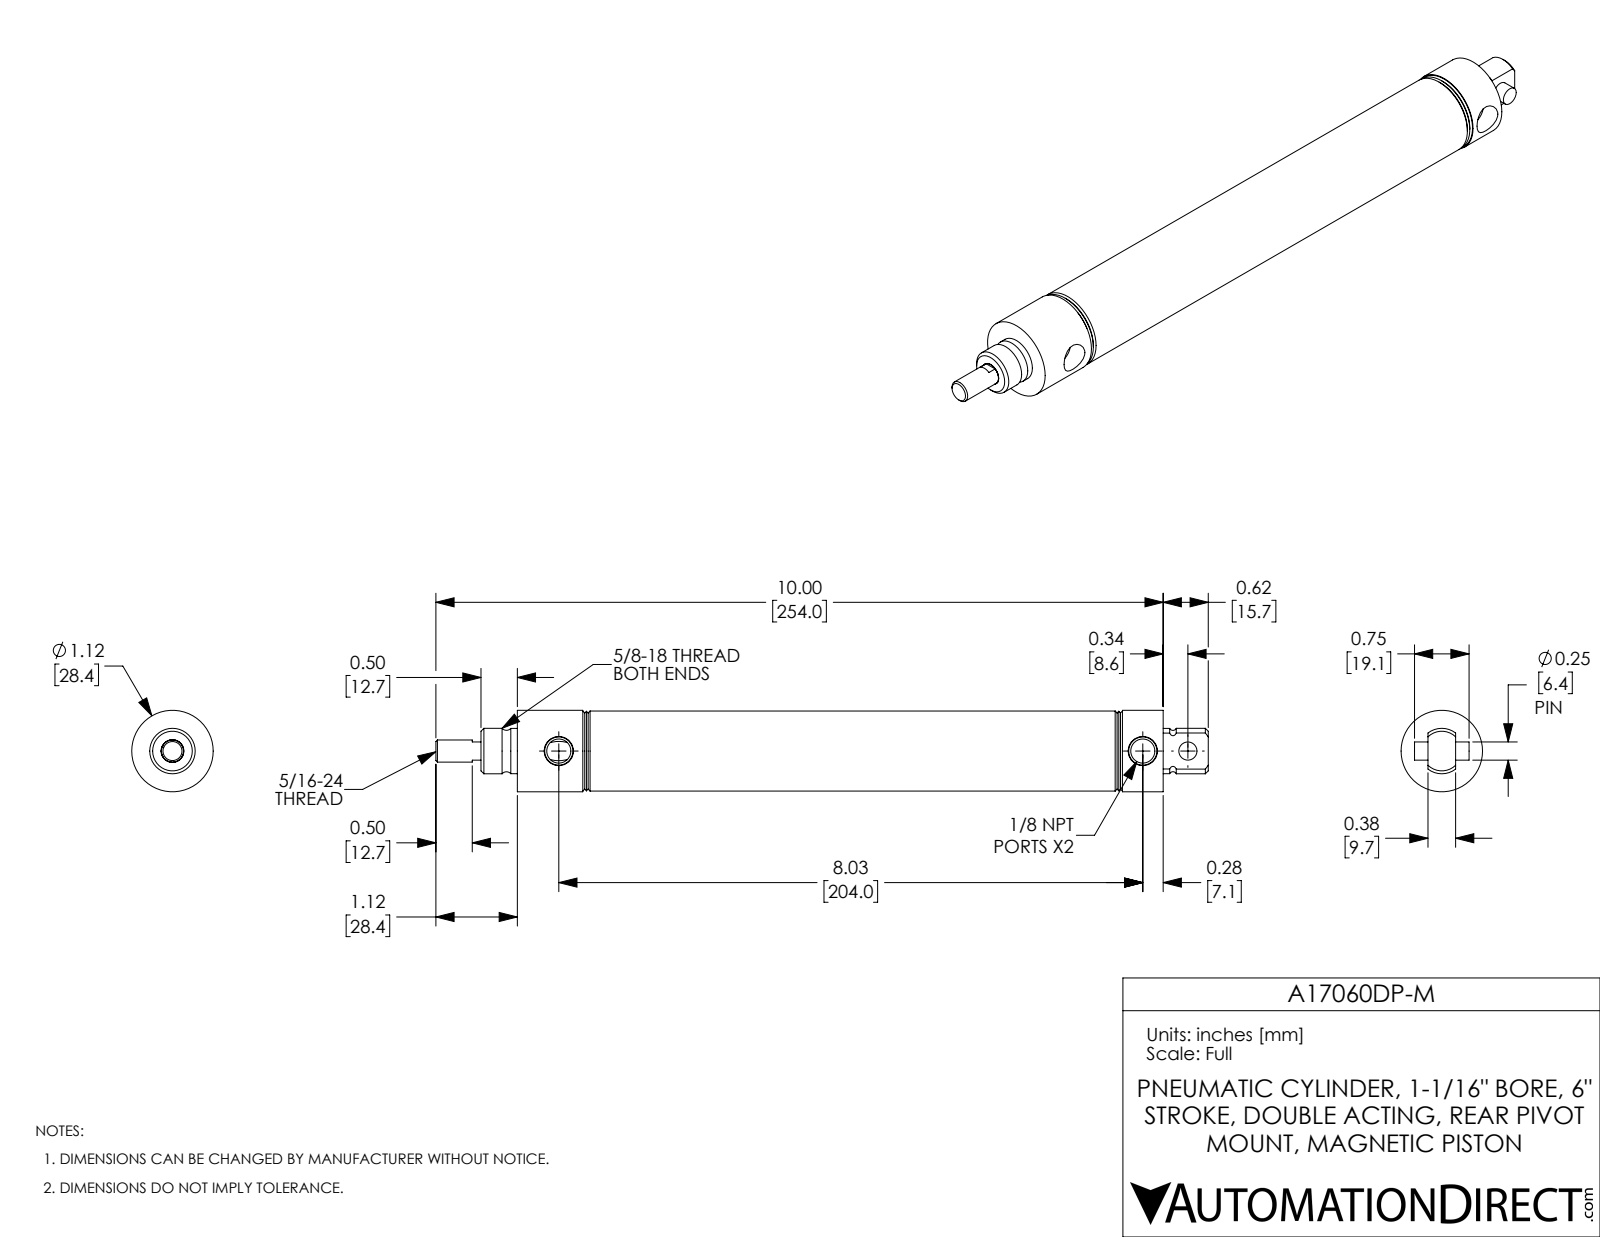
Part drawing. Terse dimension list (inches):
name: A17060DP-M-Rod; A17060DP-M-MainBody; A17060DP-M; A17060DP-M-PIN
written by: SolidWorks 2017 (AUTOMOTIVE_DESIGN)
unit: in
bodies: 3 solids, 92 faces (22 planar, 32 cylindrical, 38 other)
size: 10.62 × 1.12 × 1.12
volume: 3.867 in³; area: 73.4 in²
holes: 2× ⌀0.332, 1× ⌀0.25, 1× ⌀0.312, 1× ⌀1.063
bosses: 1× ⌀1.12, 1× ⌀1.1, 1× ⌀0.625, 1× ⌀0.623, 1× ⌀0.304
rounds: 1× R0.313
face distances: 0.5, 7.69, 6.5, 6, 1.19, 1.69, 7.69, 8.88, 7.19, 1.19
hole spacings: 0.62, 8.03, 8.65
